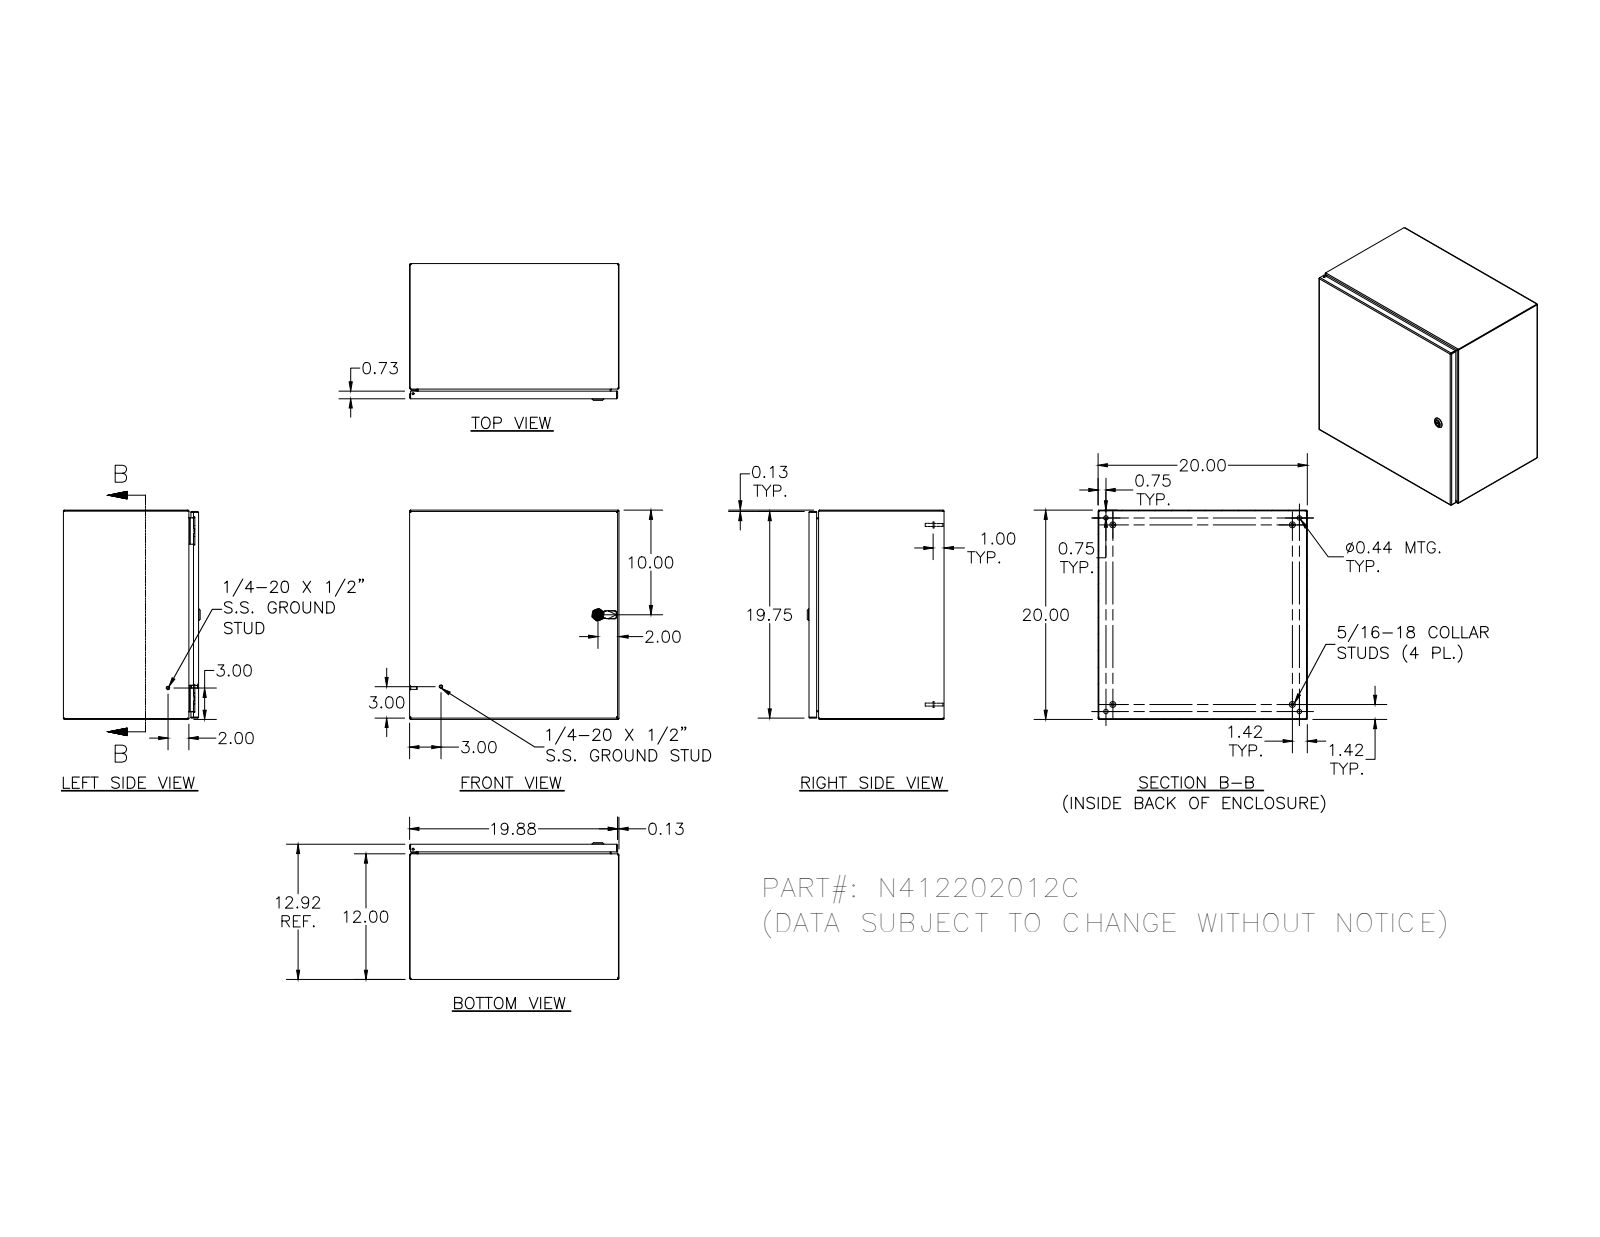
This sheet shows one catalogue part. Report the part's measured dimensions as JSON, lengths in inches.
{"part_name": "N412202012C", "step_written_by": "SolidWorks 2018 (AUTOMOTIVE_DESIGN)", "units": "inches", "bodies": {"solids": 33, "faces": 1449, "planar": 530, "cylindrical": 547, "other": 372}, "overall_size": [20, 20, 13.075], "volume_in3": 142.2, "surface_area_in2": 3863, "round_holes": [[0.188, 5], [0.093, 4], [0.152, 4], [0.167, 4], [0.172, 4], [0.437, 4], [0.156, 2], [0.187, 1], [0.197, 1], [0.315, 1], [0.394, 1], [0.402, 1]], "round_bosses_or_shafts": [[0.25, 10], [0.563, 4], [0.36, 4], [0.32, 4], [0.3, 4], [0.275, 4], [0.256, 4], [0.164, 4]], "partial_cylinders_radius": [[0.012, 30], [0.031, 30], [0.05, 26], [0.105, 20], [0.016, 18], [0.125, 16], [0.02, 13], [0.032, 8]], "face_to_face_distances": [0.074, 12.843, 19.926, 19.852, 0.074, 19.926, 20, 12.769, 12.917, 0.917], "hole_center_spacings": [16, 0.66, 0.656, 1.307, 1.965, 15.34, 15.996, 16.656]}
